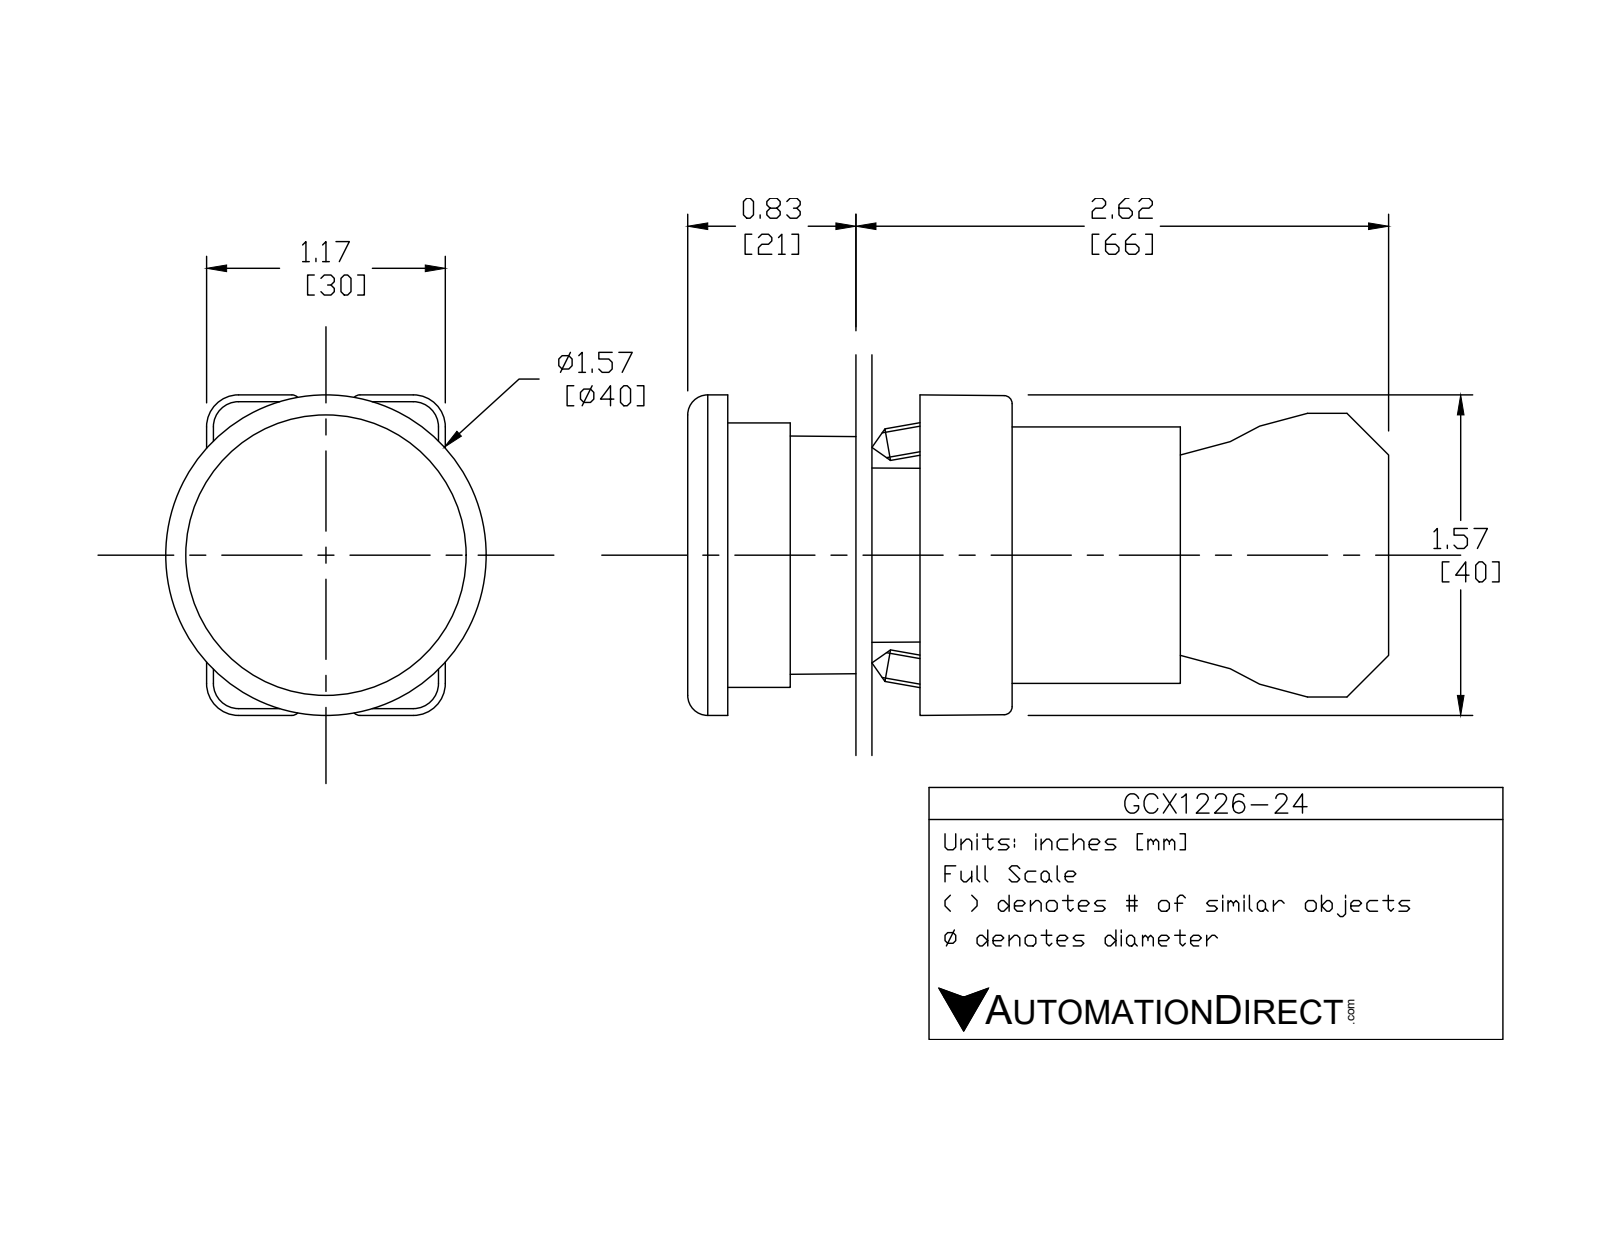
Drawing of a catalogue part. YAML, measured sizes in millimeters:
part_name: "GCX1226-24; ECX1029-2; GCX122X OPERATOR; ECX1050 (+1 more)"
step_written_by: "SolidWorks 2016 (AUTOMOTIVE_DESIGN)"
units: millimeters
bodies: {solids: 7, faces: 431, planar: 252, cylindrical: 146, other: 33}
overall_size: [88.1, 40.2, 40]
volume: 47440
surface_area: 26380
round_holes:
  - {diameter: 2, count: 2}
  - {diameter: 3.1, count: 2}
  - {diameter: 3.3, count: 2}
  - {diameter: 2.2, count: 1}
  - {diameter: 5, count: 1}
  - {diameter: 11.9, count: 1}
  - {diameter: 22.3, count: 1}
  - {diameter: 22.6, count: 1}
  - {diameter: 26, count: 1}
  - {diameter: 30, count: 1}
round_bosses_or_shafts:
  - {diameter: 4, count: 4}
  - {diameter: 33, count: 1}
  - {diameter: 29.8, count: 1}
  - {diameter: 24, count: 1}
  - {diameter: 21.7, count: 1}
  - {diameter: 19.8, count: 1}
  - {diameter: 12.8, count: 1}
partial_cylinders:
  - {radius: 1.5, count: 24}
  - {radius: 1, count: 12}
  - {radius: 3.1, count: 12}
  - {radius: 4, count: 12}
  - {radius: 1, count: 8}
  - {radius: 3.3, count: 2}
  - {radius: 0.5, count: 1}
  - {radius: 1.6, count: 1}
face_to_face_distances: [21, 62.1, 41.1, 14.7, 58.1, 37.1, 4, 14.9, 0.8, 29.6]
hole_center_spacings: [6, 13.7, 12, 12.3]
